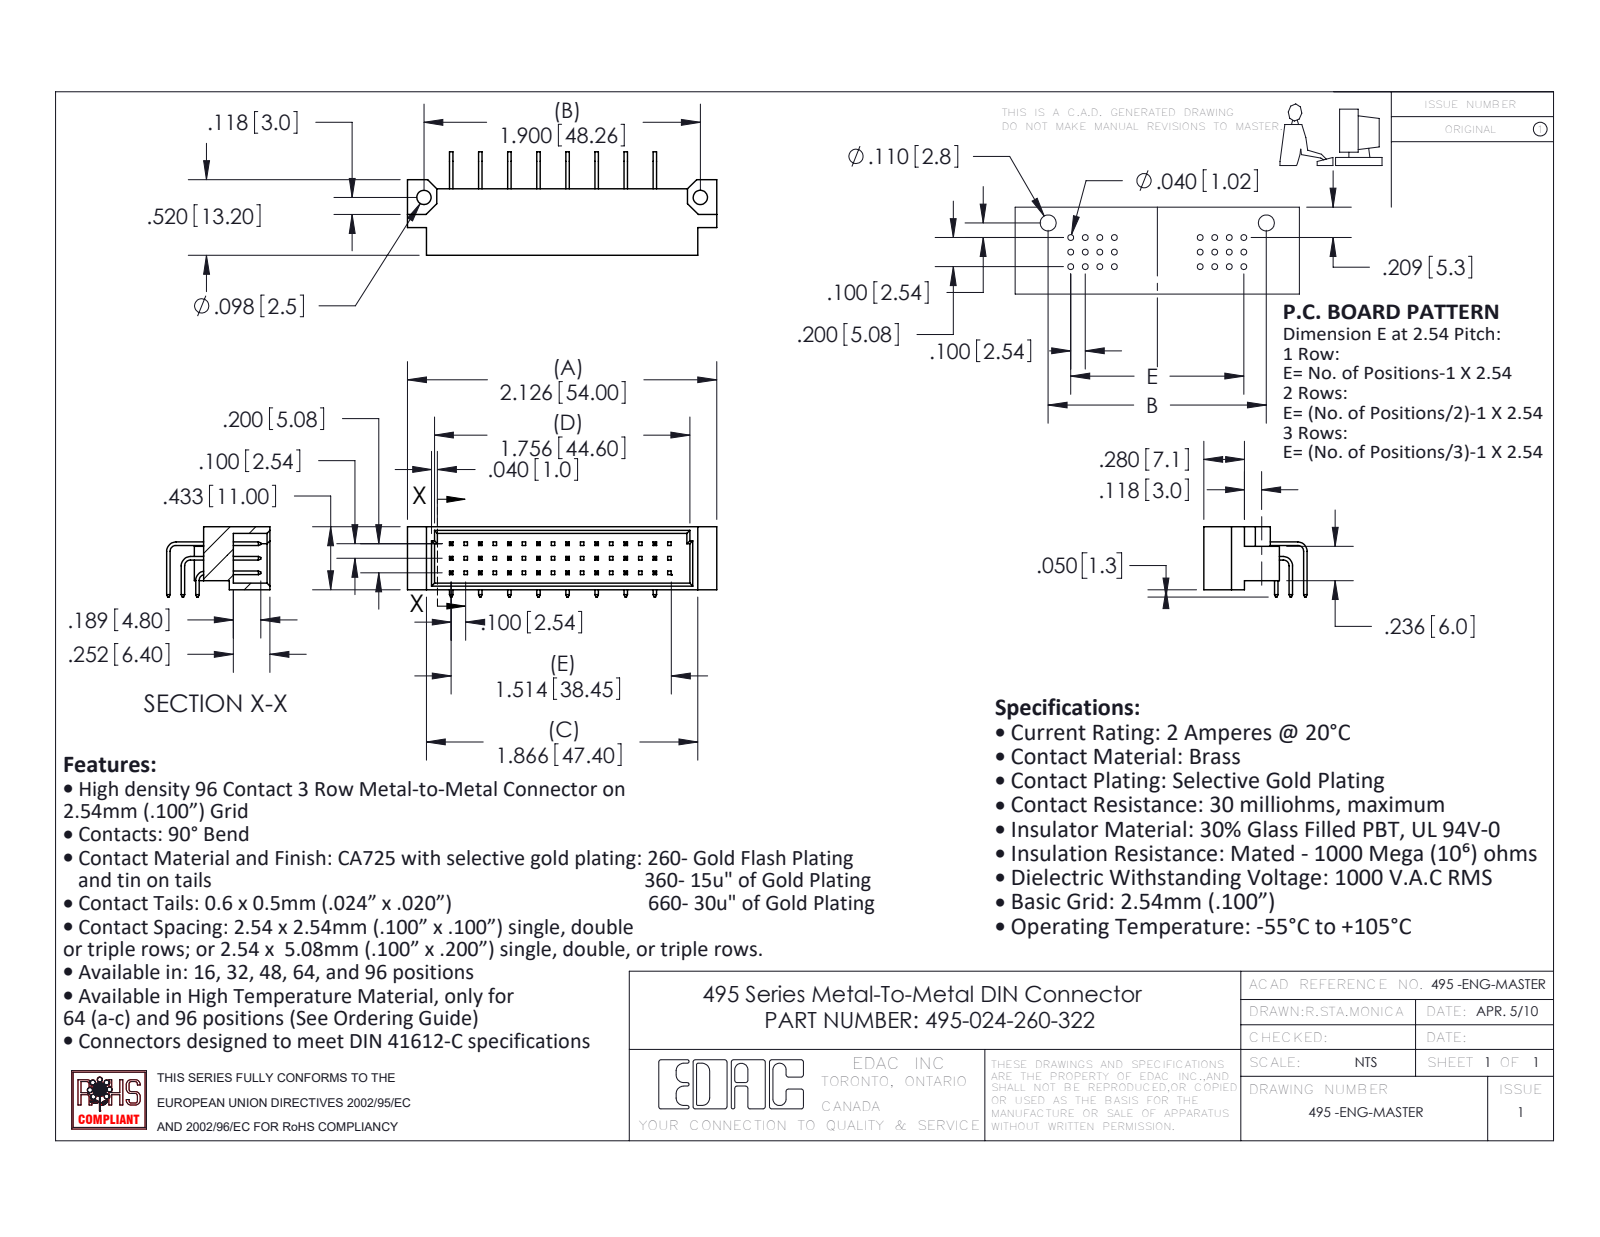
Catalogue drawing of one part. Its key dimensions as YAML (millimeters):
part_name: "495-290-1; 495-024-260-322; 495-290-3; 495-290-2 (+1 more)"
step_written_by: "SolidWorks 2020 (AUTOMOTIVE_DESIGN)"
units: millimeters
bodies: {solids: 25, faces: 674, planar: 622, cylindrical: 52, other: 0}
overall_size: [54, 18.05, 12.27]
volume: 3622
surface_area: 5113
round_holes:
  - {diameter: 2.49, count: 2}
partial_cylinders:
  - {radius: 1.02, count: 3}
  - {radius: 1.65, count: 3}
face_to_face_distances: [5.08, 10.16, 1.14, 9.86, 2.54, 5.2, 15.24, 0.61, 0.6, 20.32]
hole_center_spacings: [48.26]
